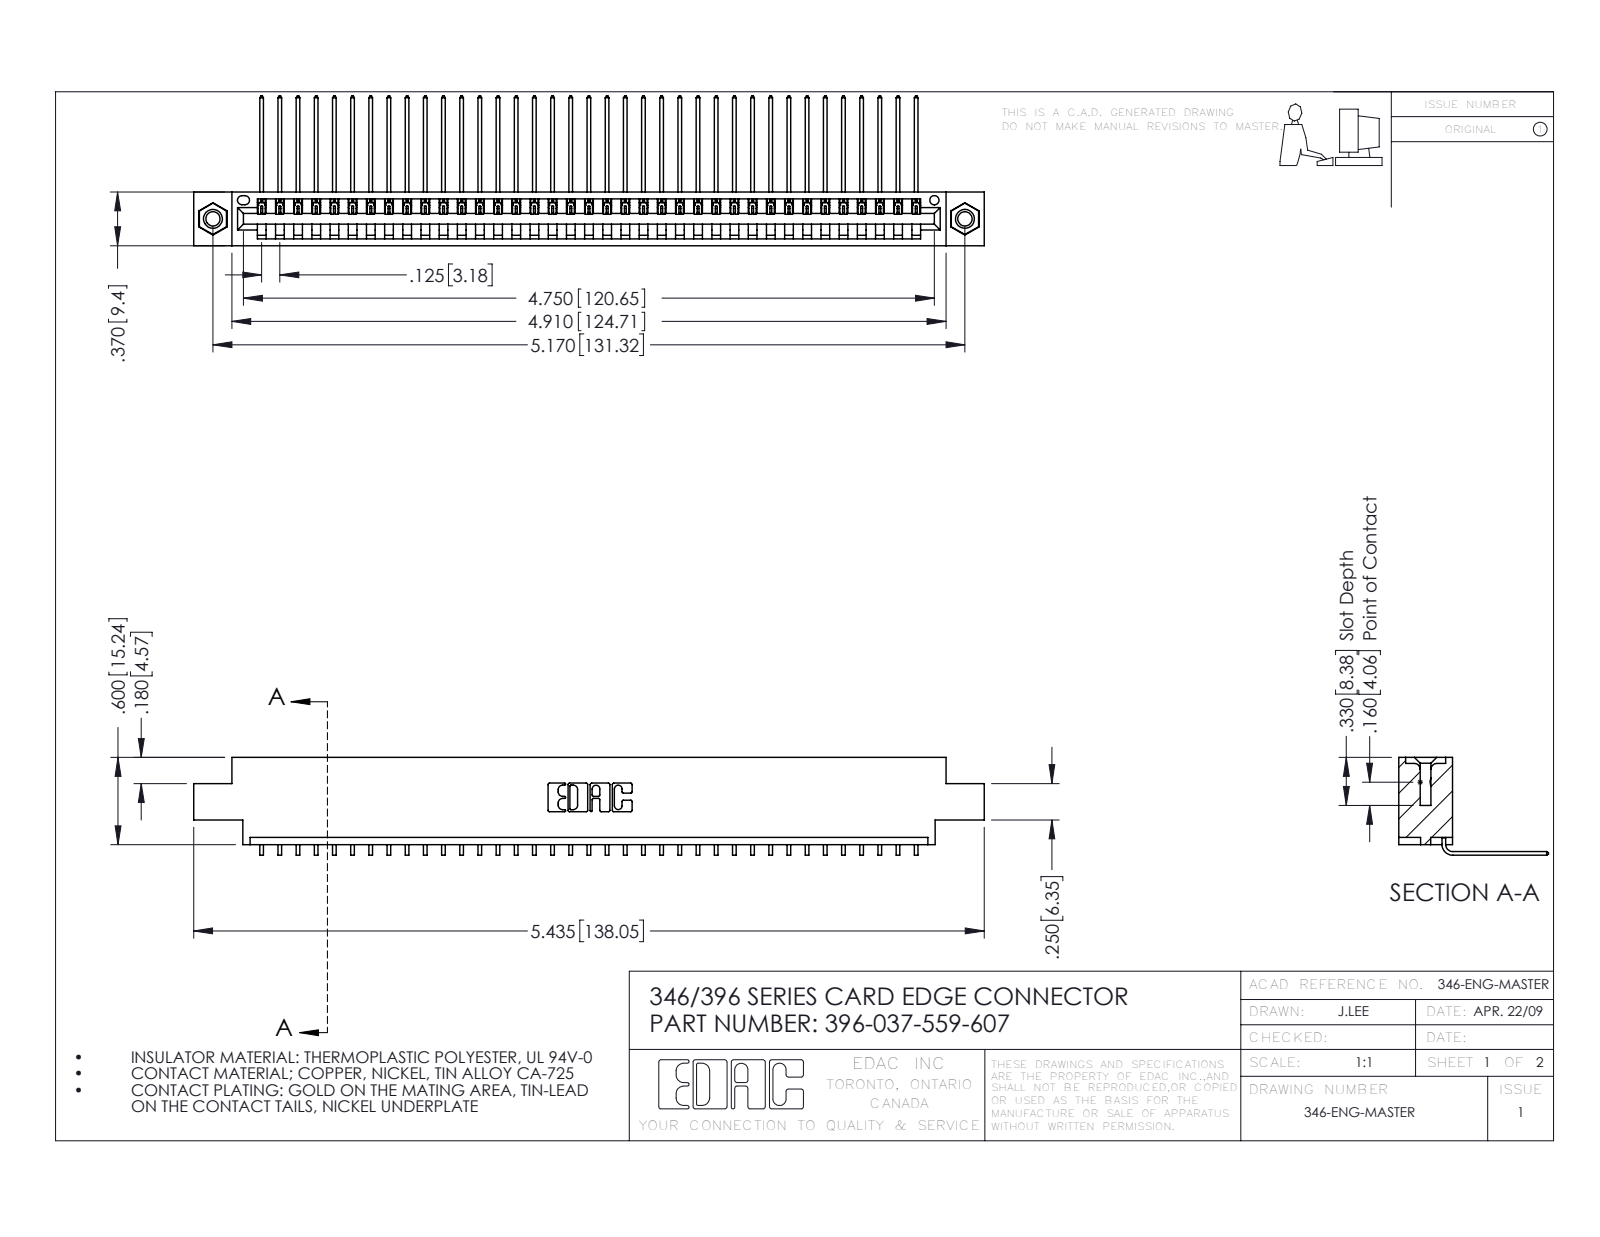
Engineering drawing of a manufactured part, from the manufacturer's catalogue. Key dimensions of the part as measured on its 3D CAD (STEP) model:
Part name (STEP PRODUCT): 346 Part_0.170 Offset - 0.156 Dia-TI; 396-037-559-607; 345-292-001_558 559 Tail - 1; 345-250-001_345-250-005-103
STEP written by: SolidWorks 2016 (CONFIG_CONTROL_DESIGN)
Units: inches
Bodies: 40 solids, 2406 faces (1666 planar, 724 cylindrical, 16 other)
Overall size (bounding box): 5.435 × 1.03 × 0.673
Volume: 0.802 in³ · Surface area: 26.81 in²
Round holes (diameter × count): ⌀0.098 ×2, ⌀0.125 ×2, ⌀0.156 ×2, ⌀0.064 ×1
Round bosses / shafts (diameter × count): ⌀0.155 ×2
Partial cylindrical surfaces — rounded edges, fillets, slot ends (radius × count): R0.006 ×74, R0.01 ×22, R0.007 ×6, R0.031 ×6, R0.026 ×3, R0.031 ×2, R0.04 ×2, R0.014 ×1
Main face-to-face distances: 0.048, 0.322, 0.37, 0.025, 0.25, 0.072, 0.222, 0.148, 0.298, 0.1
Hole centre spacings: 0.246, 4.961, 5.17
